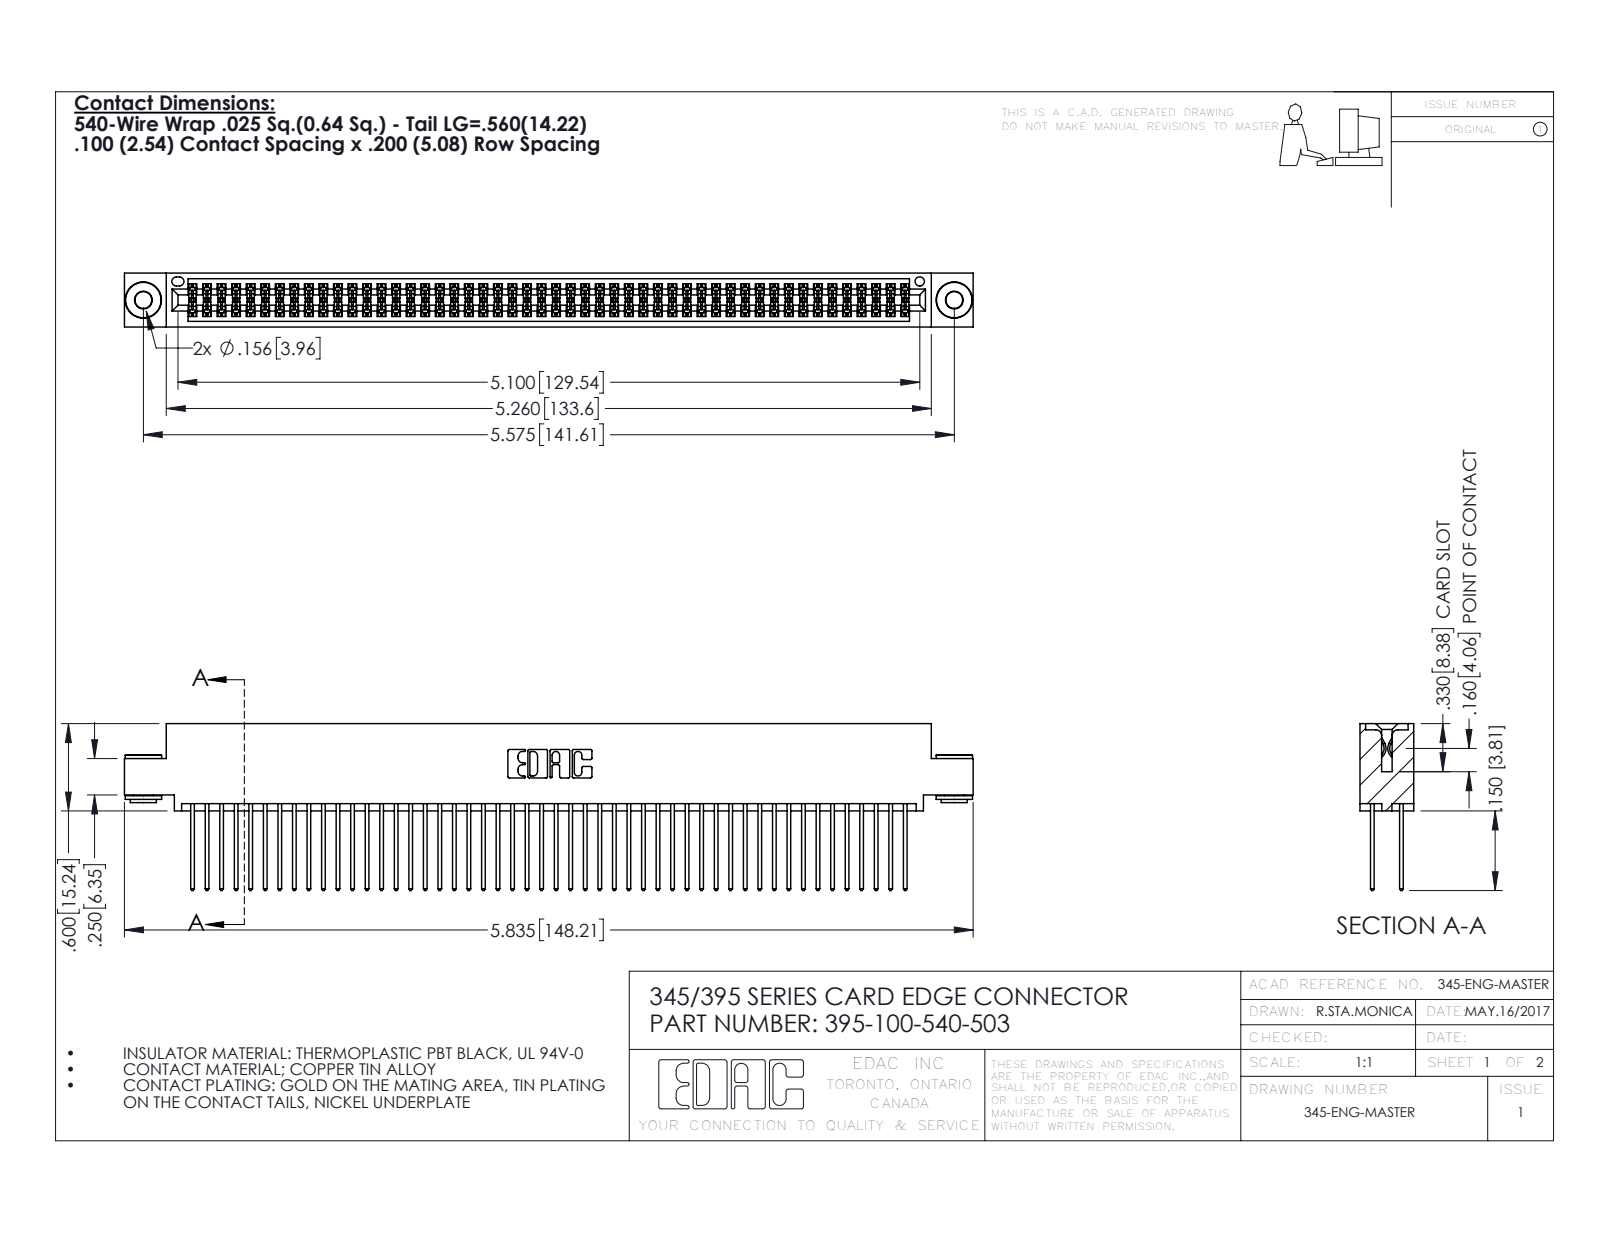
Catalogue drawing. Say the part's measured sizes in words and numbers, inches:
The part is named "345-250-002_345-250-002-102; 395-100-540-503; 345 Part_0.110 Offset - 0.156 Dia-TH; 345-292-001_345-293-140". Its 3-D file was written by "SolidWorks 2016 (CONFIG_CONTROL_DESIGN)". It is 103 solids with 5168 faces: 3394 planar, 1766 cylindrical and 8 other. Overall it measures 5.835 by 1.147 by 0.37 inches. Its volume is 0.903 cubic inches and its surface area 37.33 square inches. Round holes: 2 of diameter 0.116, 2 of diameter 0.156, 1 of diameter 0.064. Round bosses or shafts: 2 of diameter 0.25, 2 of diameter 0.18, 2 of diameter 0.136. Partial cylindrical surfaces (rounded edges, fillets, slot ends): 150 of radius 0.006, 100 of radius 0.01, 22 of radius 0.01, 6 of radius 0.007, 6 of radius 0.031, 3 of radius 0.026, 2 of radius 0.014, 2 of radius 0.019. The main face-to-face distances are 0.072, 0.298, 0.2, 0.025, 0.098, 0.272, 0.37, 0.225, 0.175, 0.149. The hole center spacings are 0.27, 5.339, 5.575.
